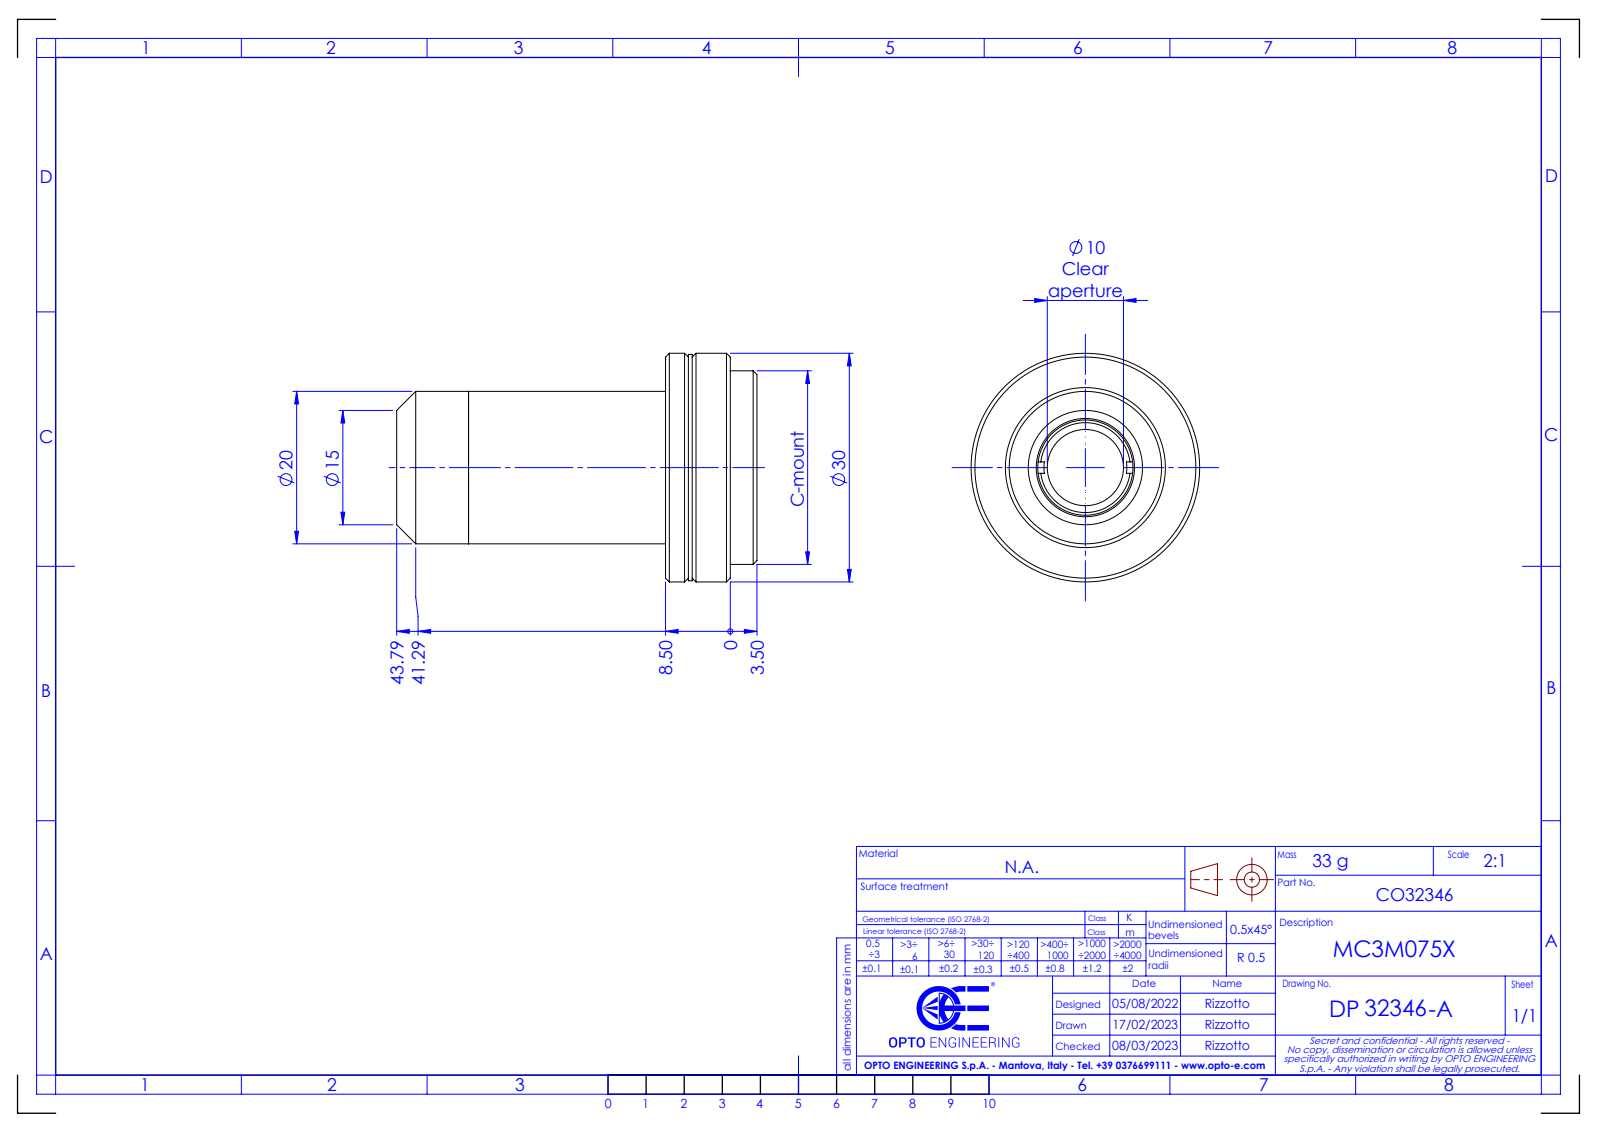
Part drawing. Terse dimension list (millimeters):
name: DP32346-A_MC3M075X
written by: SolidWorks 2021 (CONFIG_CONTROL_DESIGN)
unit: mm
bodies: 0 solids, 66 faces (18 planar, 22 cylindrical, 26 other)
size: 47.29 × 30 × 30
holes: 1× ⌀10, 1× ⌀12.5, 1× ⌀15.5, 1× ⌀18
bosses: 1× ⌀30, 1× ⌀29.7, 1× ⌀25.4, 1× ⌀20
face distances: 8.5, 3.5, 5, 3, 0.5, 5.5, 12, 9, 25.86, 28.86
